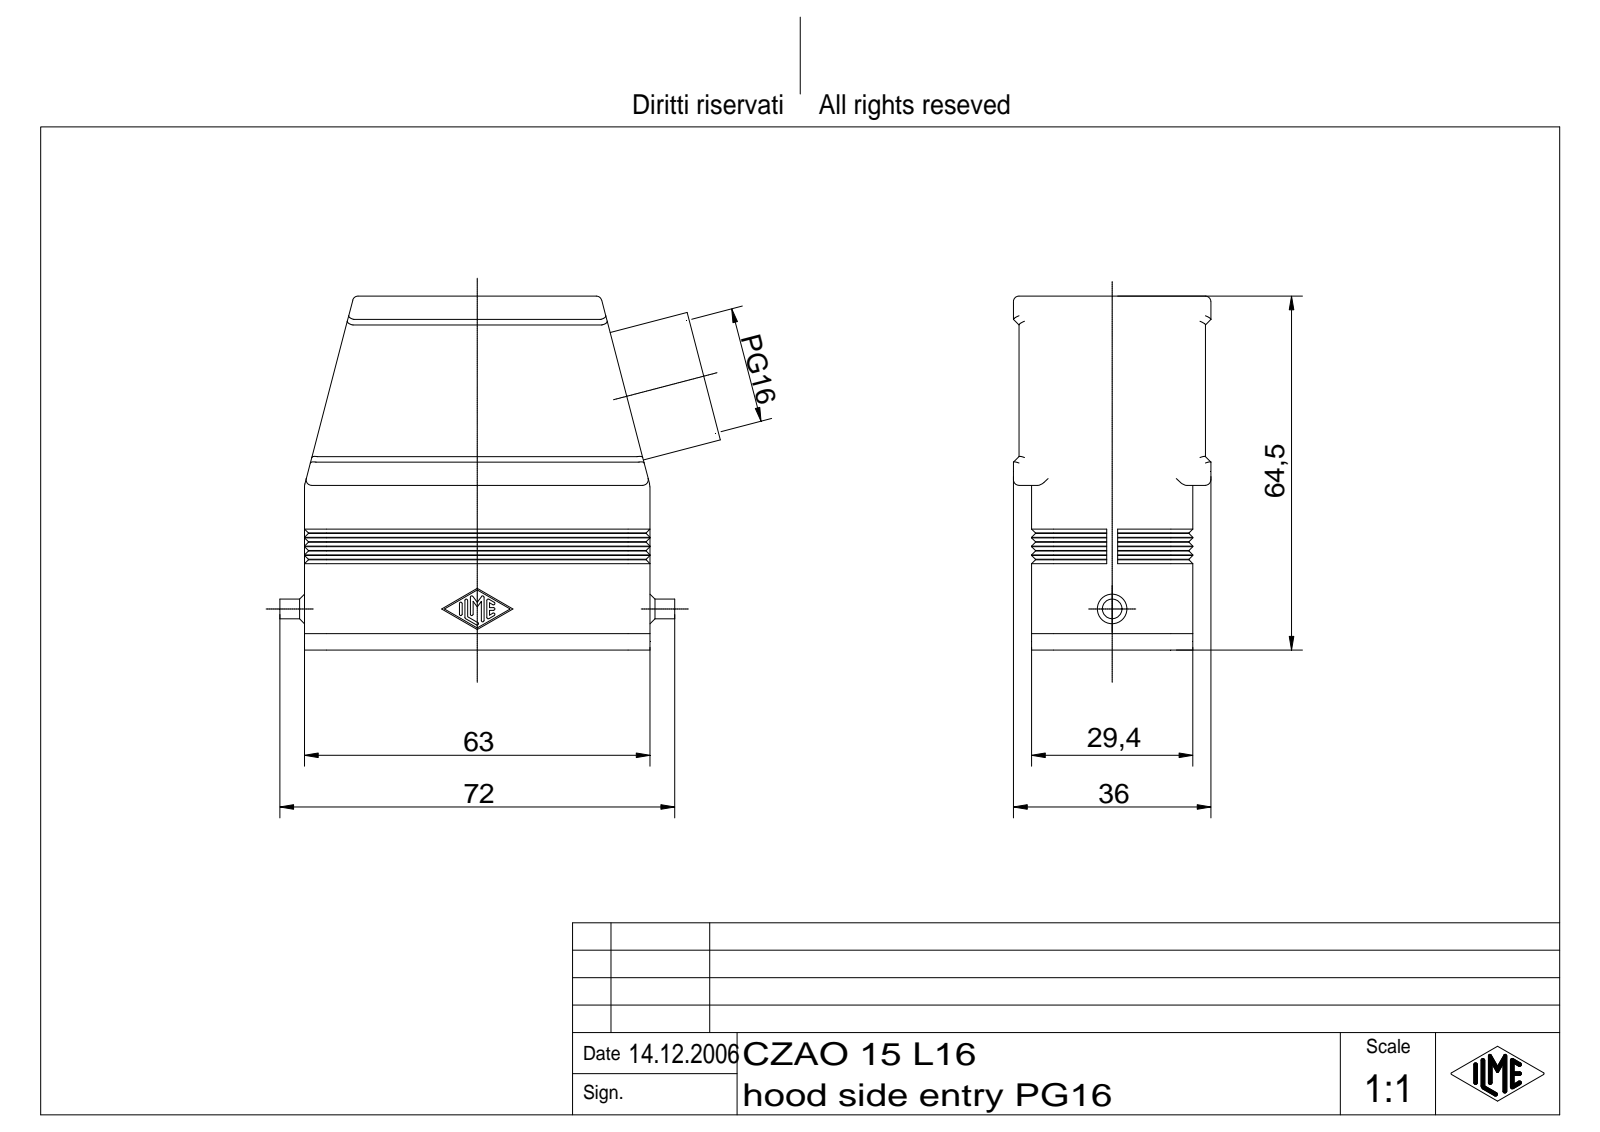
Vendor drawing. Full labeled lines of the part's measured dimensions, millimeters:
Part name (STEP PRODUCT): CZ_MZ Tüllengehäuse 1 Bügel
STEP written by: Autodesk Inventor 7 (AUTOMOTIVE_DESIGN)
Units: millimetres
Bodies: 1 solid, 412 faces (170 planar, 146 cylindrical, 96 other)
Overall size (bounding box): 80.32 × 64.5 × 36
Volume: 48 875 mm³ · Surface area: 28 394 mm²
Round holes (diameter × count): ⌀2.46 ×4, ⌀3.5 ×4, ⌀19.16 ×1, ⌀21.16 ×1, ⌀24 ×1
Round bosses / shafts (diameter × count): ⌀24 ×1, ⌀23 ×1, ⌀3.6 ×1
Partial cylindrical surfaces — rounded edges, fillets, slot ends (radius × count): R1 ×24, R0.25 ×14, R4 ×8, R2 ×6, R1.25 ×4, R3.3 ×2
Main face-to-face distances: 3, 26.4, 23.4, 29.4, 2.3, 28.7, 5.3, 31.7, 10, 50
Hole centre spacings: 16, 49.5, 52.02
